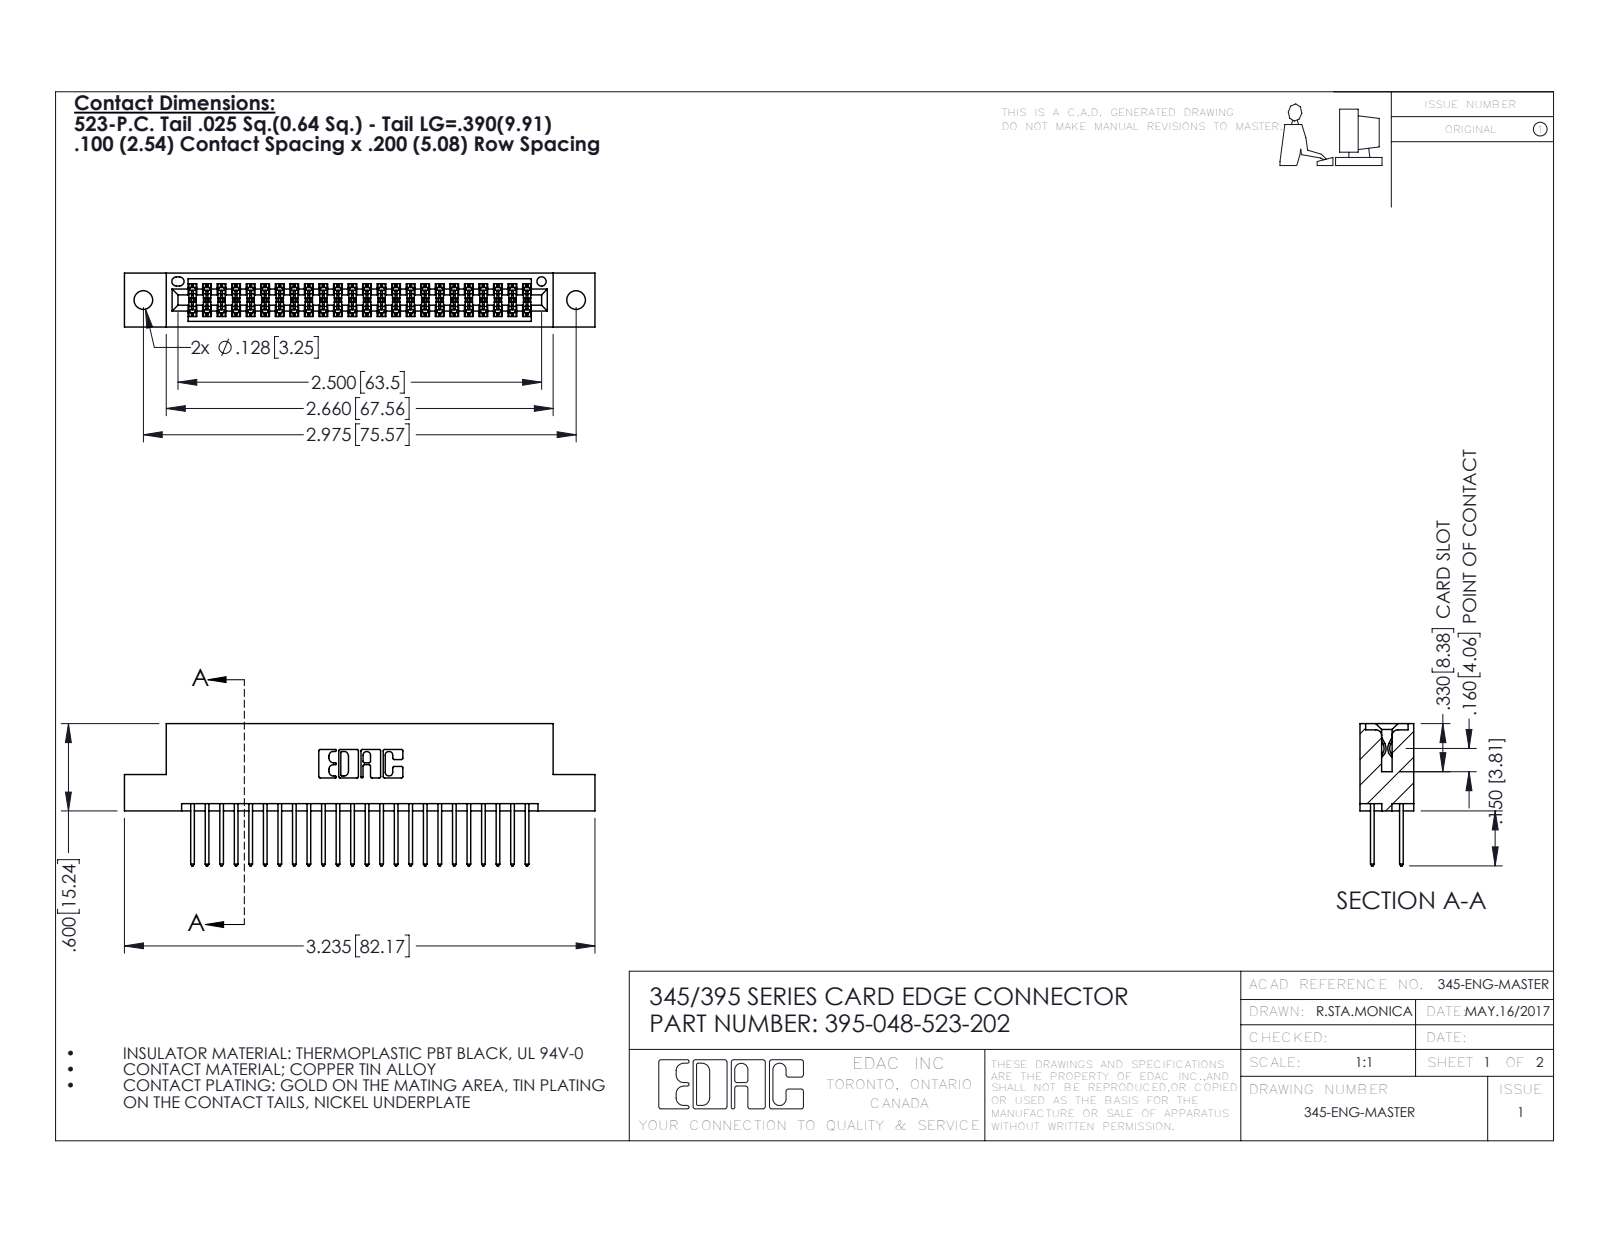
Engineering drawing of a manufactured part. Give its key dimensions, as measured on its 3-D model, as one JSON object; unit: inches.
{"part_name": "345-292-001_345-293-123; 345 Part_Flush Mounting Lugs - 0.128 Dia; 395-048-523-202", "step_written_by": "SolidWorks 2016 (CONFIG_CONTROL_DESIGN)", "units": "inches", "bodies": {"solids": 49, "faces": 2526, "planar": 1664, "cylindrical": 862, "other": 0}, "overall_size": [3.235, 0.977, 0.37], "volume_in3": 0.481, "surface_area_in2": 17.77, "round_holes": [[0.128, 2], [0.064, 1]], "partial_cylinders_radius": [[0.006, 72], [0.01, 48], [0.01, 22], [0.007, 6], [0.031, 6], [0.026, 3], [0.014, 2], [0.019, 2]], "face_to_face_distances": [0.298, 0.072, 0.2, 0.098, 0.272, 0.025, 0.37, 0.225, 0.175, 0.149], "hole_center_spacings": [0.27, 2.741, 2.975]}
